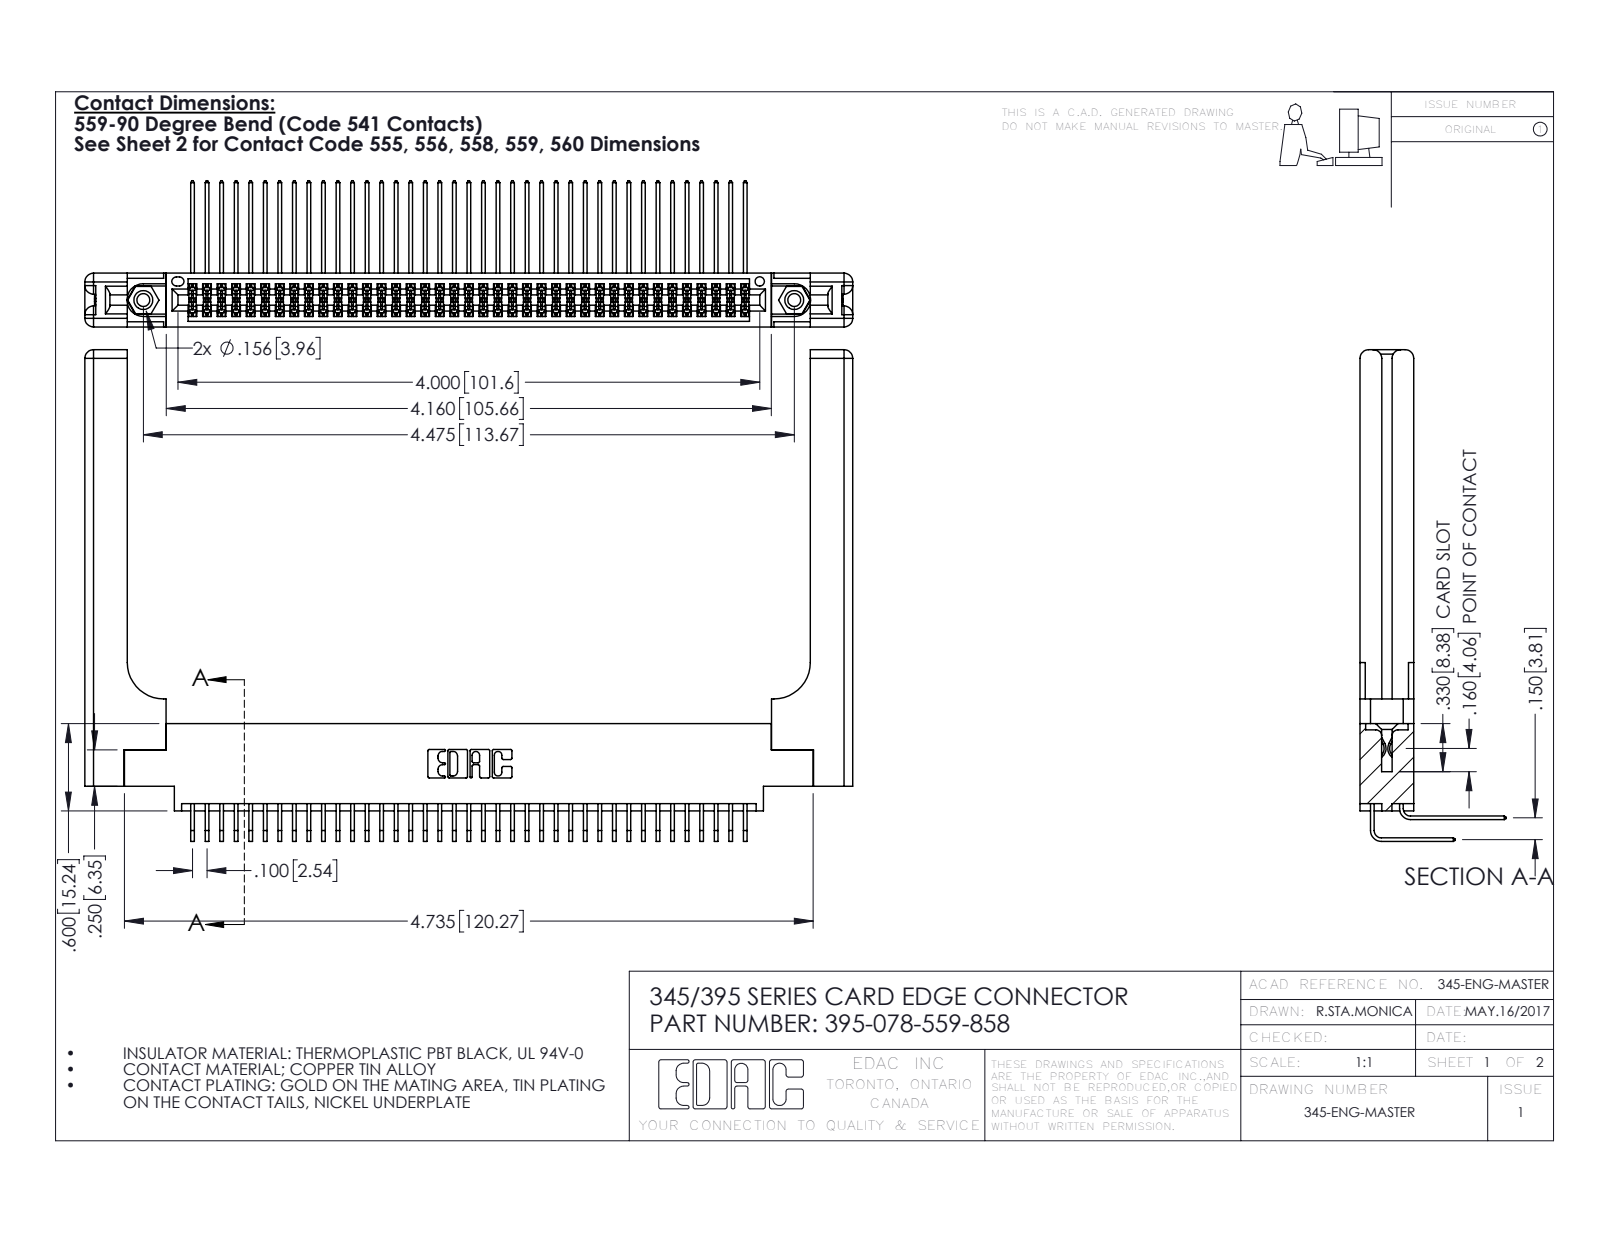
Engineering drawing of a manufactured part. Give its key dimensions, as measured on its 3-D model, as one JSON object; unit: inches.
{"part_name": "345-250-001_345-250-001-102; 345-292-001_558 559 Tail - 1; 395-078-559-858; 345 Part_0.170 Offset - 0.156 Dia-TH (+2 more)", "step_written_by": "SolidWorks 2016 (CONFIG_CONTROL_DESIGN)", "units": "inches", "bodies": {"solids": 83, "faces": 4442, "planar": 2962, "cylindrical": 1420, "other": 60}, "overall_size": [5.279, 3.379, 1.005], "volume_in3": 1.331, "surface_area_in2": 41.8, "round_holes": [[0.089, 2], [0.125, 2], [0.156, 2], [0.064, 1]], "round_bosses_or_shafts": [[0.155, 2]], "partial_cylinders_radius": [[0.006, 117], [0.01, 22], [0.06, 16], [0.007, 6], [0.031, 6], [0.026, 3], [0.014, 2], [0.019, 2]], "face_to_face_distances": [0.072, 0.37, 0.298, 0.098, 0.272, 0.025, 0.2, 0.225, 0.15, 0.175], "hole_center_spacings": [0.27, 4.239, 4.475]}
